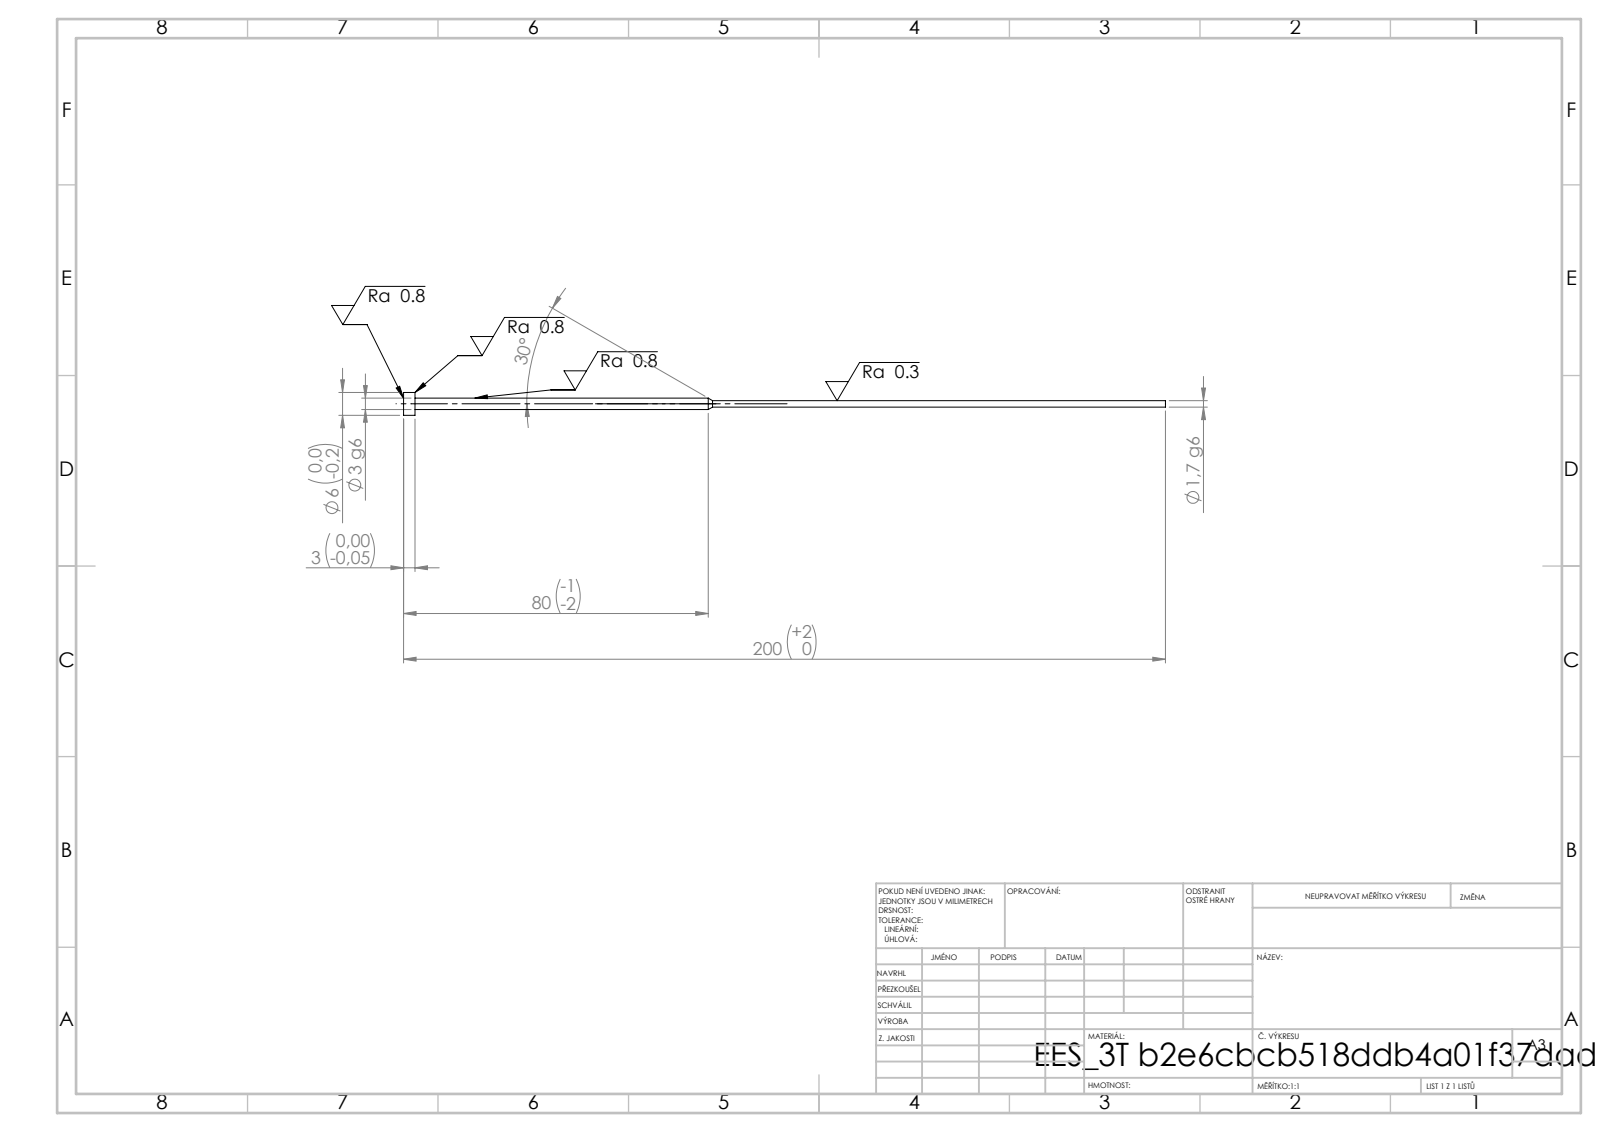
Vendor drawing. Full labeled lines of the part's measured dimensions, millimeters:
STEP written by: SolidWorks 2019 (CONFIG_CONTROL_DESIGN)
Units: millimetres
Bodies: 1 solid, 11 faces (3 planar, 6 cylindrical, 2 other)
Overall size (bounding box): 200 × 6 × 6
Volume: 904 mm³ · Surface area: 1 478 mm²
Round bosses / shafts (diameter × count): ⌀6 ×1, ⌀3 ×1, ⌀1.7 ×1
Main face-to-face distances: 3, 197, 200
